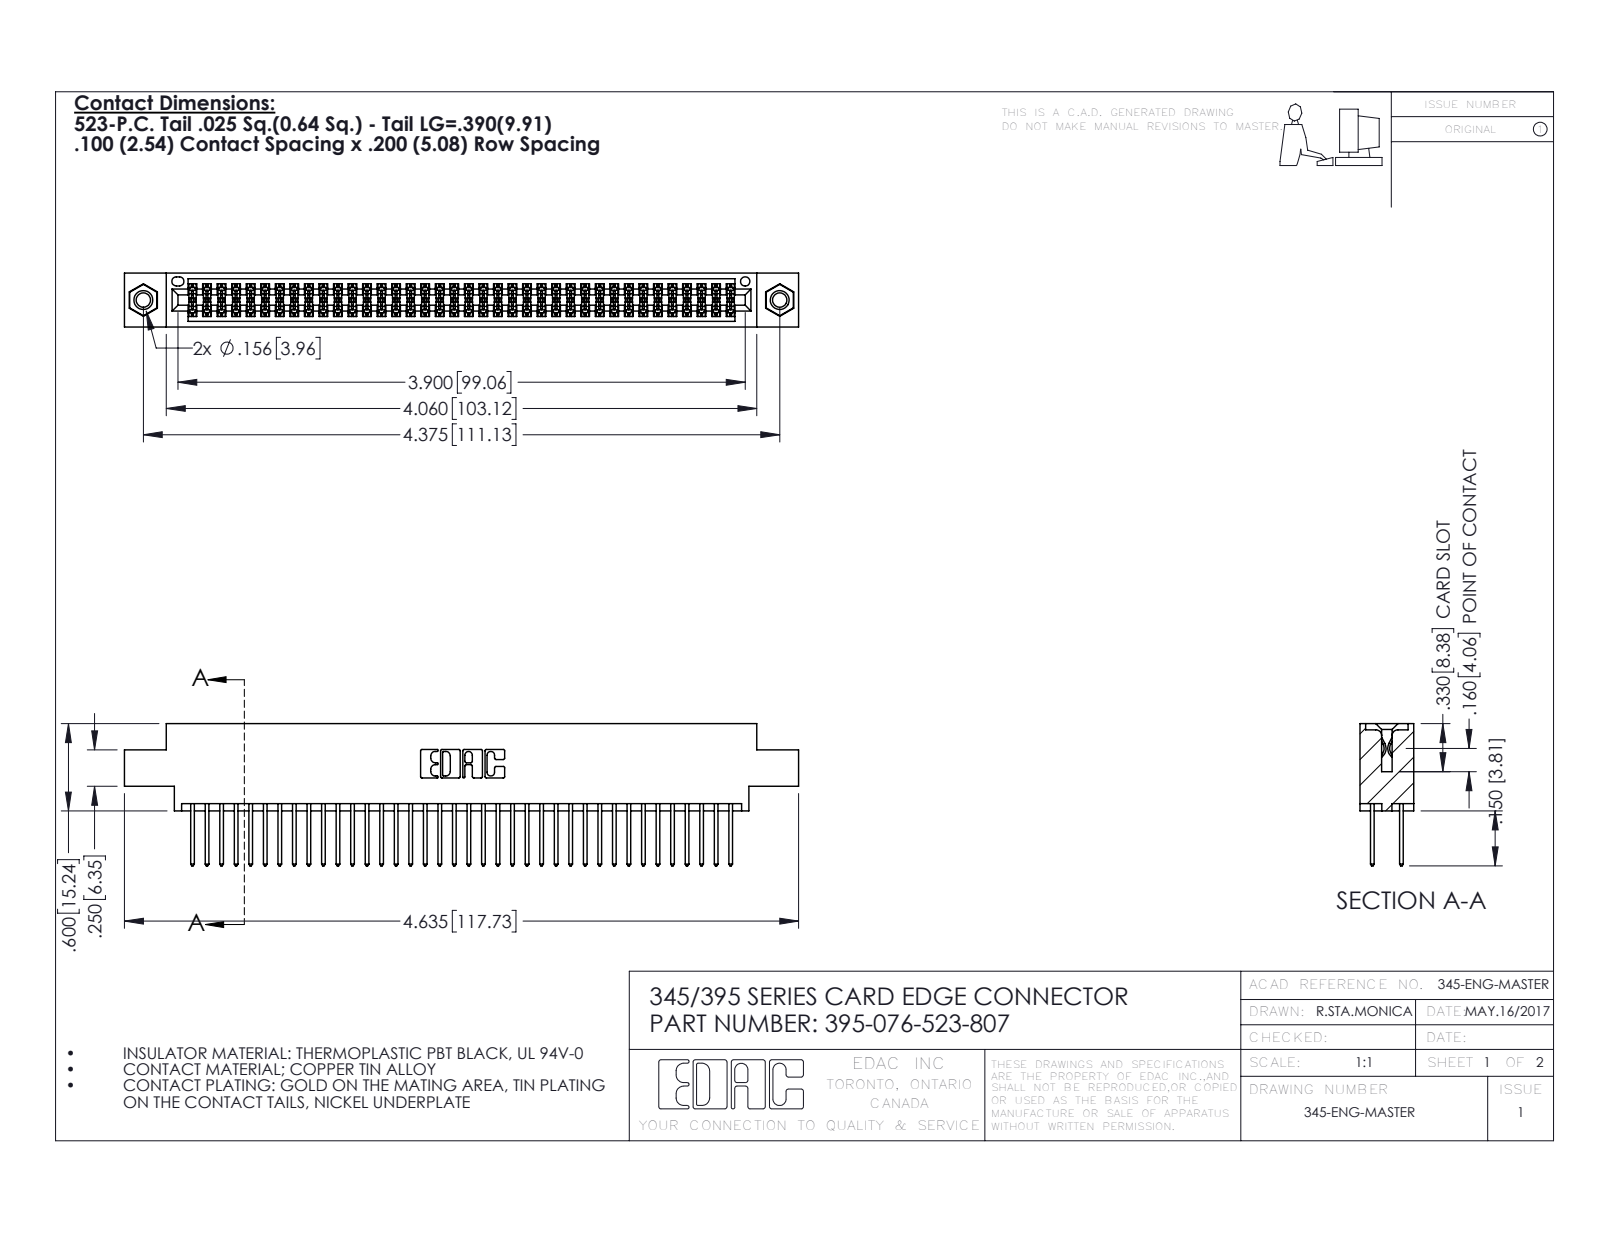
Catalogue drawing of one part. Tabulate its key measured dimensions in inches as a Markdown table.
| quantity | value |
| --- | --- |
| part name | 345 Part_0.170 Offset - 0.156 Dia-TI; 395-076-523-807; 345-292-001_345-293-123; 345-250-001_345-250-005-103 |
| STEP written by | SolidWorks 2016 (CONFIG_CONTROL_DESIGN) |
| units | inches |
| bodies | 79 solids, 3990 faces (2624 planar, 1350 cylindrical, 16 other) |
| overall size | 4.635 × 0.977 × 0.37 |
| volume | 0.697 in³ |
| surface area | 27.41 in² |
| round holes (diameter × count) | 0.098 × 2, 0.125 × 2, 0.156 × 2, 0.064 × 1 |
| round bosses / shafts (diameter × count) | 0.155 × 2 |
| partial cylindrical surfaces (radius × count) | 0.006 × 114, 0.01 × 76, 0.01 × 22, 0.007 × 6, 0.031 × 6, 0.026 × 3, 0.014 × 2, 0.019 × 2 |
| main face-to-face distances | 0.072, 0.298, 0.2, 0.098, 0.272, 0.025, 0.37, 0.225, 0.175, 0.149 |
| hole center spacings | 0.27, 4.139, 4.375 |
